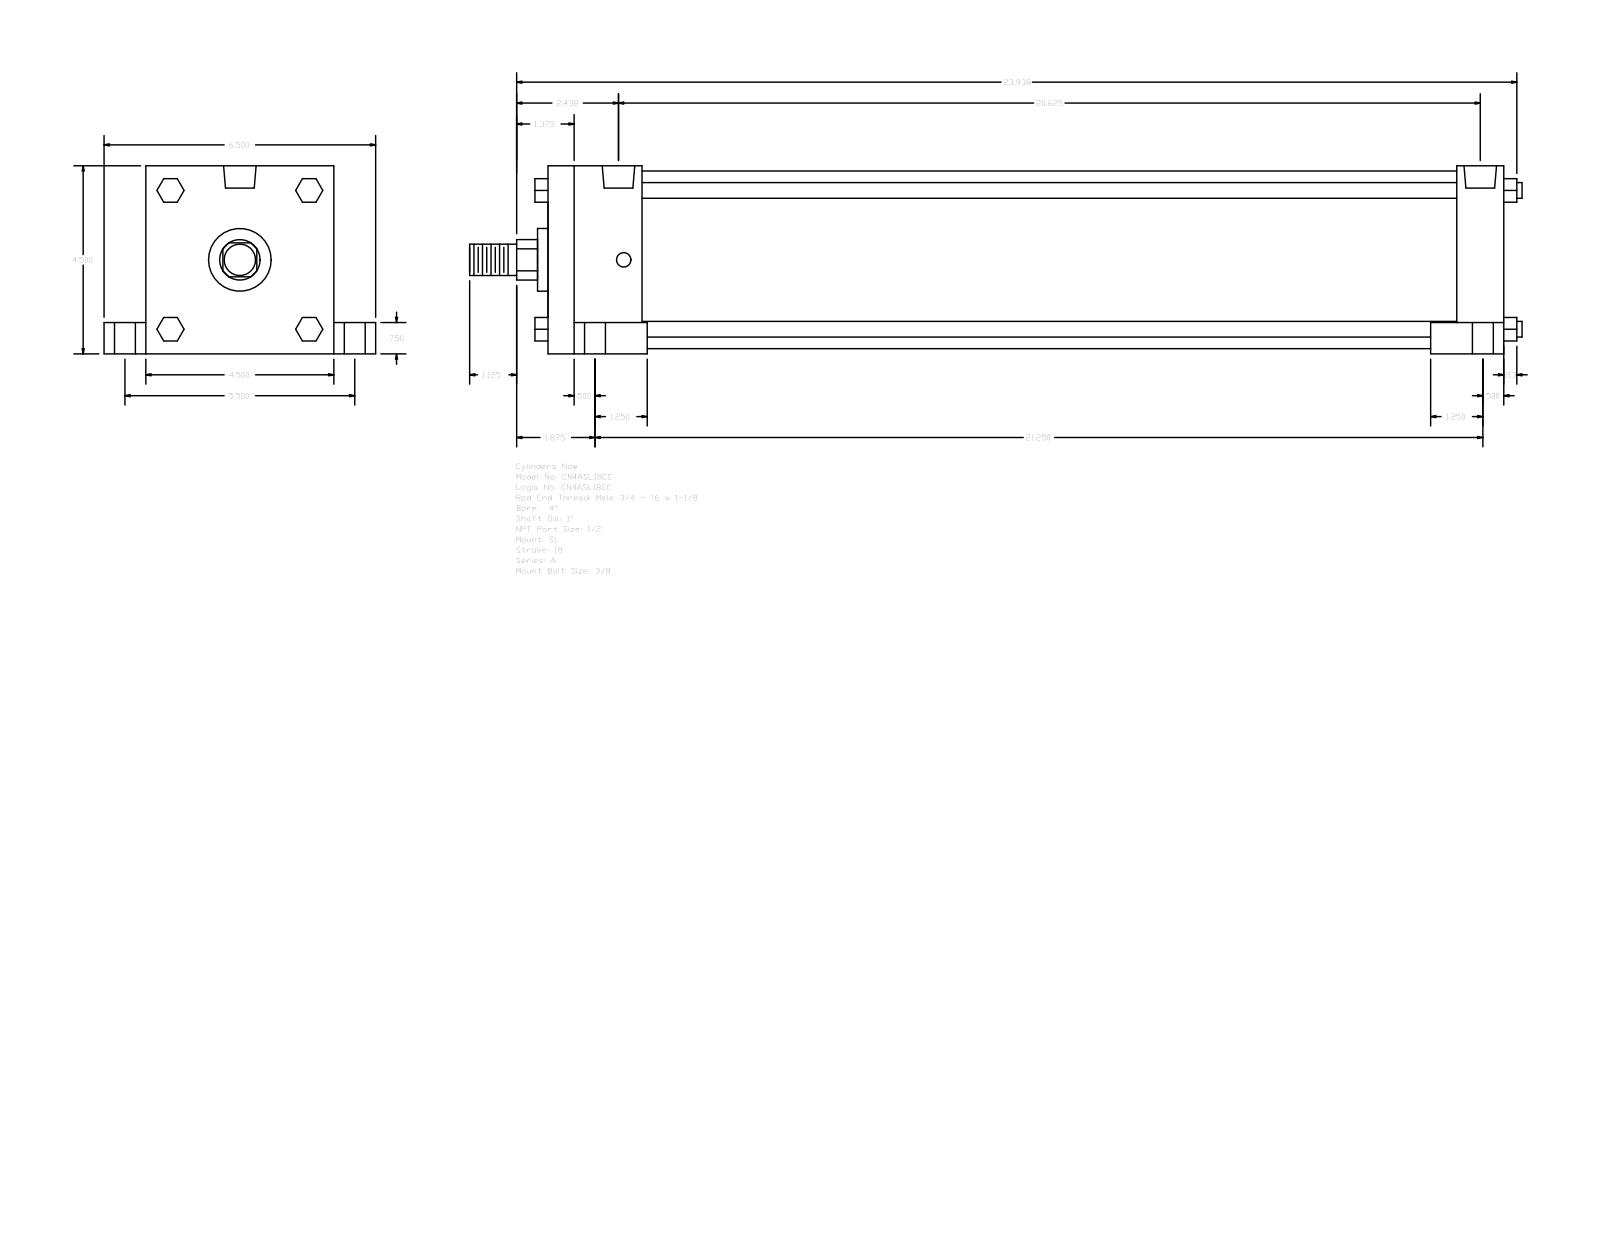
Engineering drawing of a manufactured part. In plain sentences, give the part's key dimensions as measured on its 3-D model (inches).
The part is named "A_SL__0400_1". Its 3-D file was written by "GSSL Pune (CONFIG_CONTROL_DESIGN)". It is 0 solids with 150 faces: 114 planar, 36 cylindrical and 0 other. Overall it measures 25.187 by 6.5 by 4.5 inches. Round holes: 4 of diameter 0.344, 4 of diameter 0.5, 4 of diameter 0.75, 2 of diameter 0.778. Round bosses or shafts: 4 of diameter 0.375, 1 of diameter 4.25, 1 of diameter 1.5, 1 of diameter 1, 1 of diameter 0.75. Partial cylindrical surfaces (rounded edges, fillets, slot ends): 1 of radius 0.484. The main face-to-face distances are 4.5, 22.875, 2.25, 20.625, 21.75, 19.5, 1.125, 0.75, 1, 5.5. The hole center spacings are 0.125, 2.751, 2.756, 2.807, 2.835, 5.5, 20.375, 20.5.
